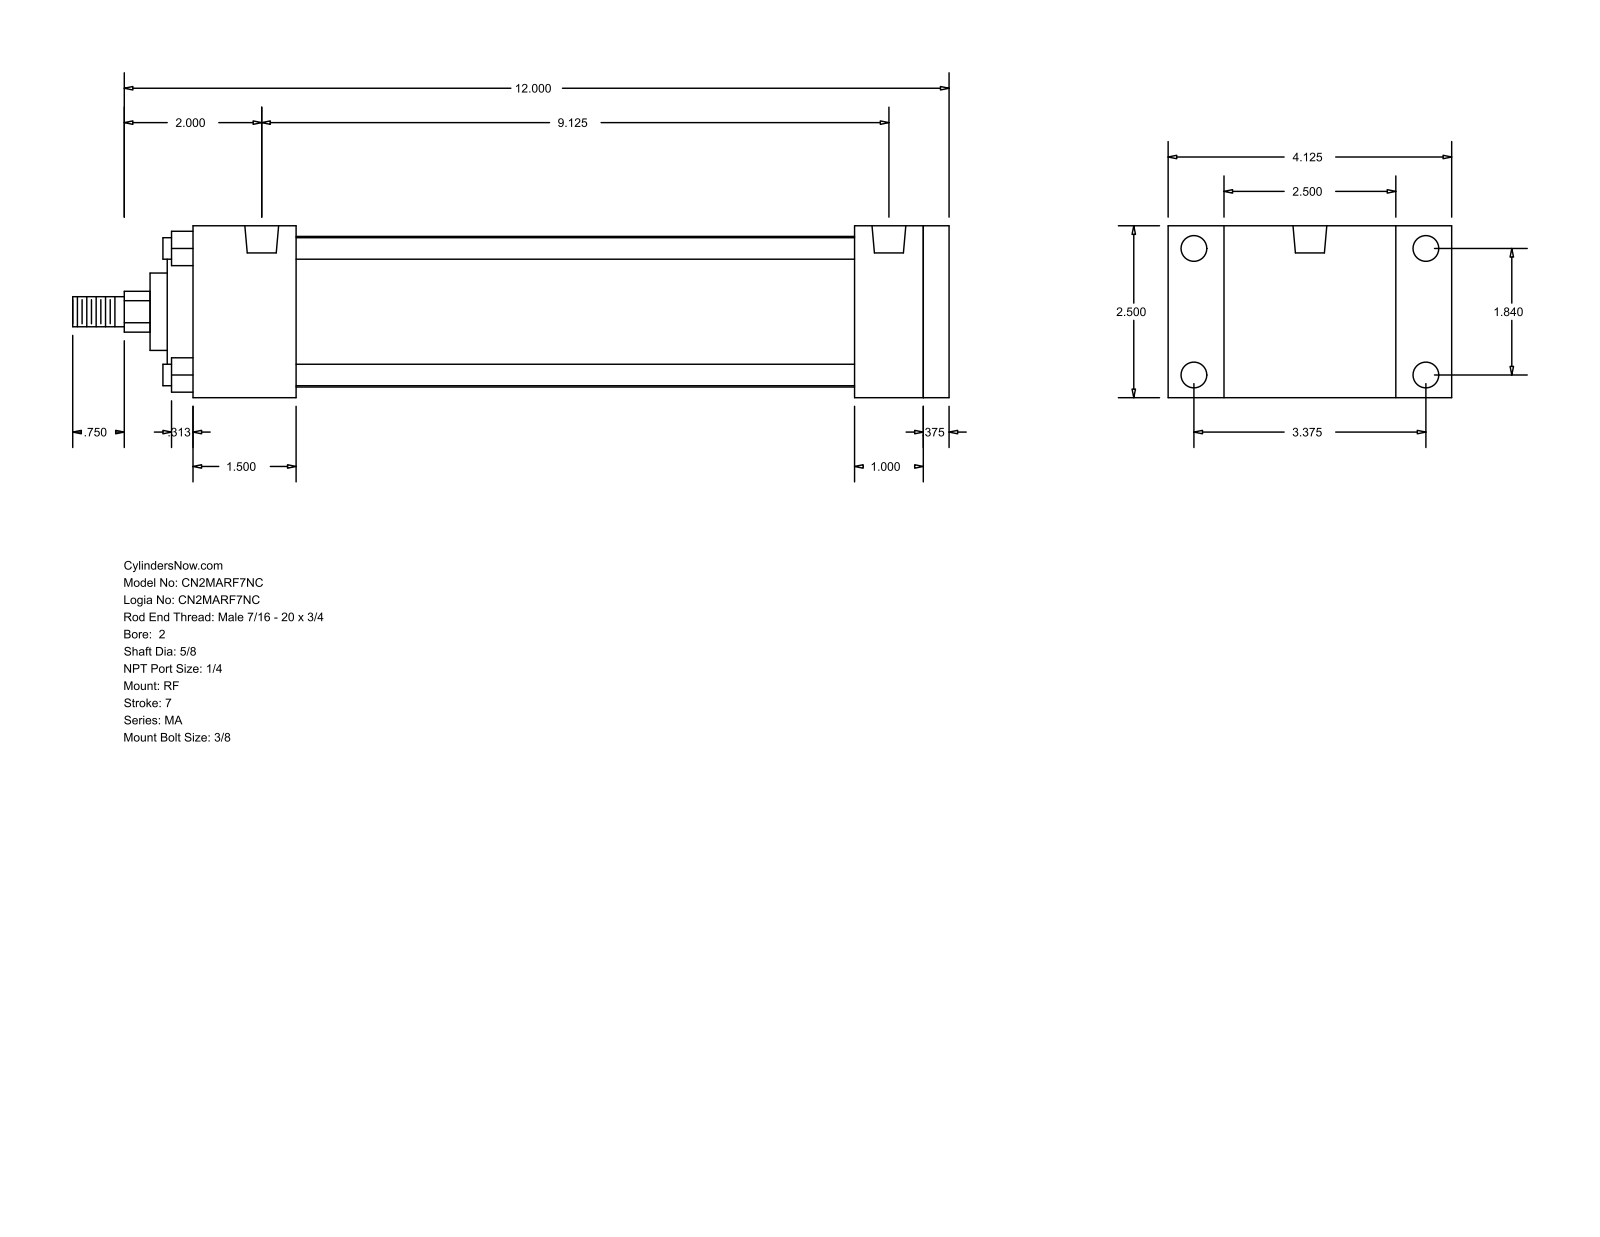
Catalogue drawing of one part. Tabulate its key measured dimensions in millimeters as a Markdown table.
| quantity | value |
| --- | --- |
| part name | MA_RF__0200_0.625 |
| STEP written by | GSSL Pune (CONFIG_CONTROL_DESIGN) |
| units | millimeters |
| bodies | 0 solids, 94 faces (65 planar, 29 cylindrical, 0 other) |
| overall size | 323.85 × 104.78 × 63.5 |
| round holes (diameter × count) | 7.94 × 4, 9.53 × 4, 12.49 × 2 |
| round bosses / shafts (diameter × count) | 7.94 × 4, 55.63 × 1, 50.8 × 1, 28.57 × 1, 15.88 × 1, 11.11 × 1 |
| partial cylindrical surfaces (radius × count) | 7.54 × 1 |
| main face-to-face distances | 63.5, 9.53, 38.1, 269.87, 279.4, 288.92, 231.77, 241.3, 244.48, 206.38 |
| hole center spacings | 46.74, 85.72, 97.63, 231.77 |
